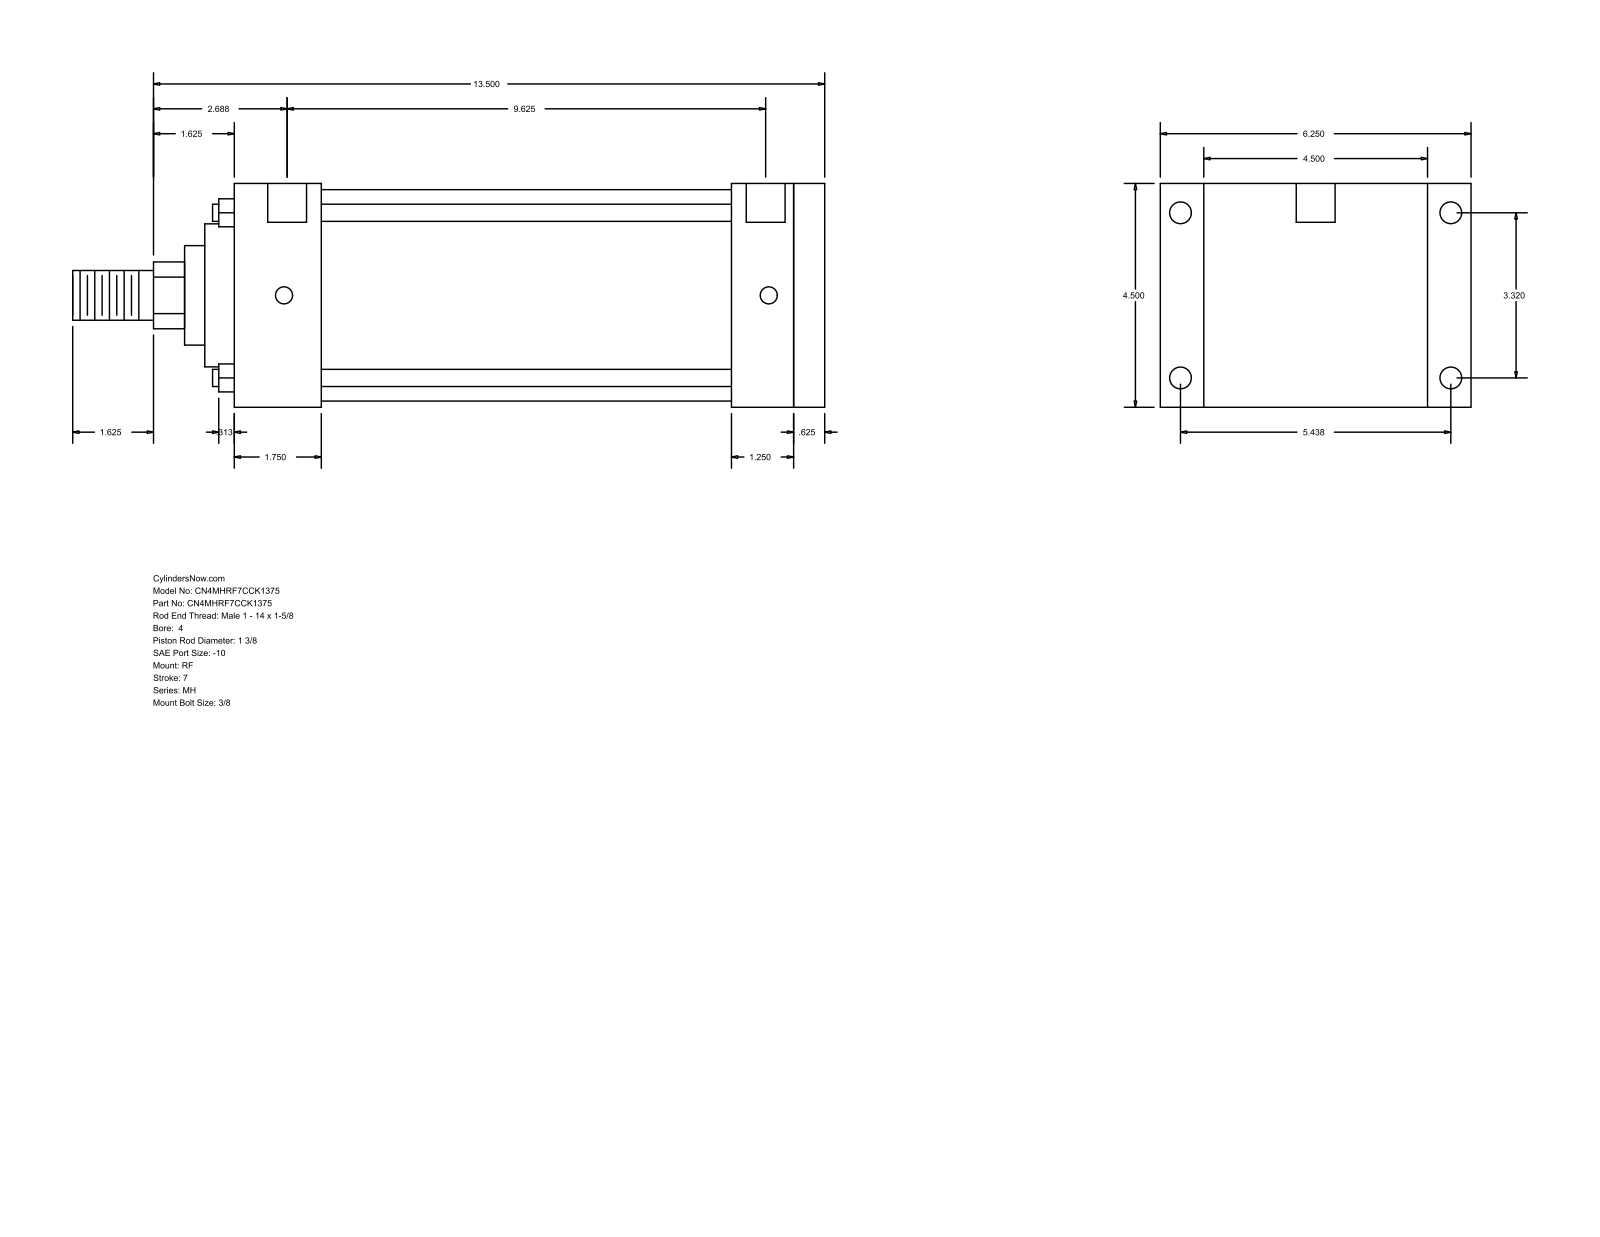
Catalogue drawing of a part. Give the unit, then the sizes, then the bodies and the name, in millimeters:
Units: millimetres
Overall size (bounding box): 384.18 × 158.75 × 114.3
Round holes (diameter × count): ⌀8.73 ×4, ⌀11.13 ×4, ⌀19.84 ×2
Round bosses / shafts (diameter × count): ⌀8.76 ×4, ⌀107.95 ×1, ⌀73.03 ×1, ⌀50.8 ×1, ⌀34.92 ×1, ⌀25.4 ×1
Partial cylindrical surfaces — rounded edges, fillets, slot ends (radius × count): R17.06 ×1
Main face-to-face distances: 114.3, 301.63, 15.88, 285.75, 44.45, 241.3, 257.18, 254, 209.55, 31.75
Hole centre spacings: 84.32, 138.12, 161.82, 247.65, 1.58, 1.59, 244.48, 246.06
Bodies: 0 solids, 94 faces (65 planar, 29 cylindrical, 0 other)
Part name (STEP PRODUCT): MH_RF__0400_1.375
STEP written by: GSSL Pune (CONFIG_CONTROL_DESIGN)
